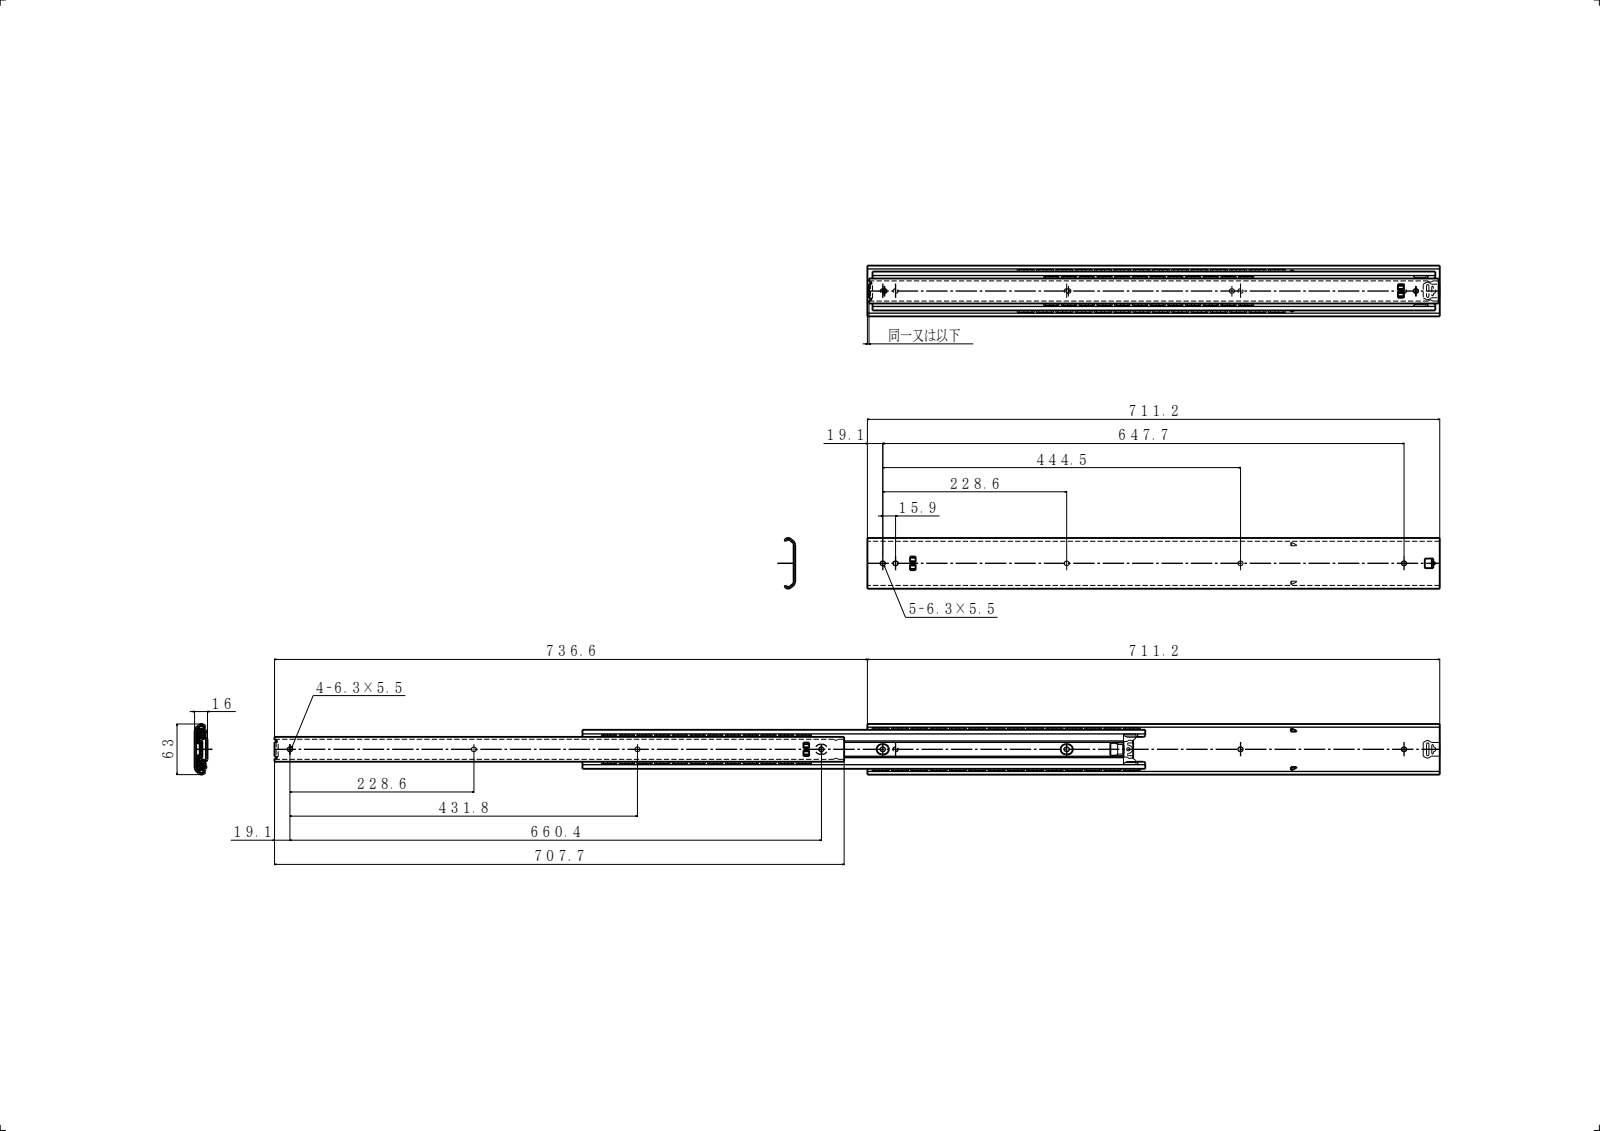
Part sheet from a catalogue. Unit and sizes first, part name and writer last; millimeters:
Units: millimetres
Overall size (bounding box): 1448.34 × 63 × 16
Round holes (diameter × count): ⌀5.4 ×1
Round bosses / shafts (diameter × count): ⌀5 ×1
Partial cylindrical surfaces — rounded edges, fillets, slot ends (radius × count): R1 ×22, R0.5 ×18, R2.75 ×18, R2 ×16, R0.3 ×12, R1.2 ×10, R0.2 ×8, R1.6 ×8
Main face-to-face distances: 2, 14, 1.56, 12, 16, 4.08, 1.3, 12.7, 2.86, 11.14
Volume: 281 823 mm³ · Surface area: 320 250 mm²
Bodies: 10 solids, 635 faces (392 planar, 241 cylindrical, 2 other)
Part name (STEP PRODUCT): PN68; PN48B; C630-28; C630-28 OM (+5 more)
STEP written by: SolidWorks 2019 (CONFIG_CONTROL_DESIGN)
